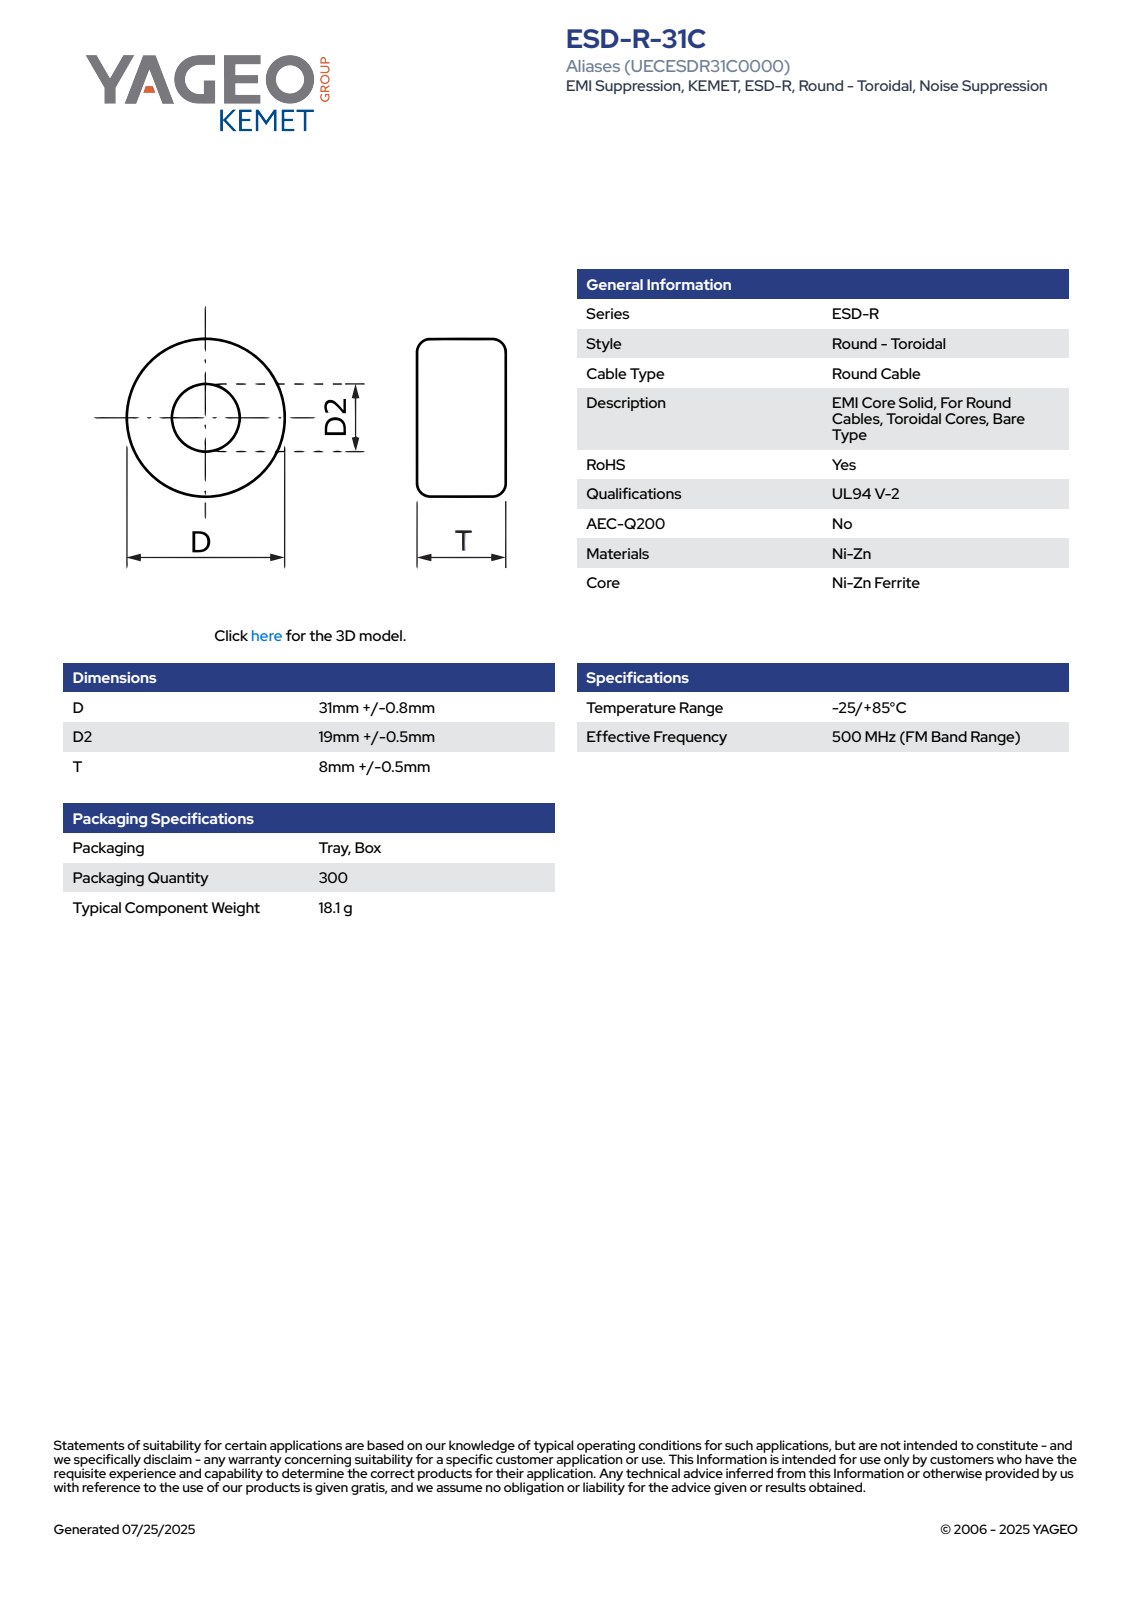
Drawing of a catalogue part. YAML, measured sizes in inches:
part_name: "EC_KBC_D31.8D219T8.5"
step_written_by: "SolidWorks 2021 (AUTOMOTIVE_DESIGN)"
units: inches
bodies: {solids: 1, faces: 66, planar: 24, cylindrical: 7, other: 35}
overall_size: [1.252, 1.252, 0.335]
volume: 0.262
surface_area: 3.567
round_holes:
  - {diameter: 0.748, count: 1}
round_bosses_or_shafts:
  - {diameter: 1.252, count: 1}
partial_cylinders:
  - {radius: 0.626, count: 1}
face_to_face_distances: [0.335, 0.134, 0.201, 0.067, 0.013, 0.146, 0.188, 0.054, 0.042, 0.176]
